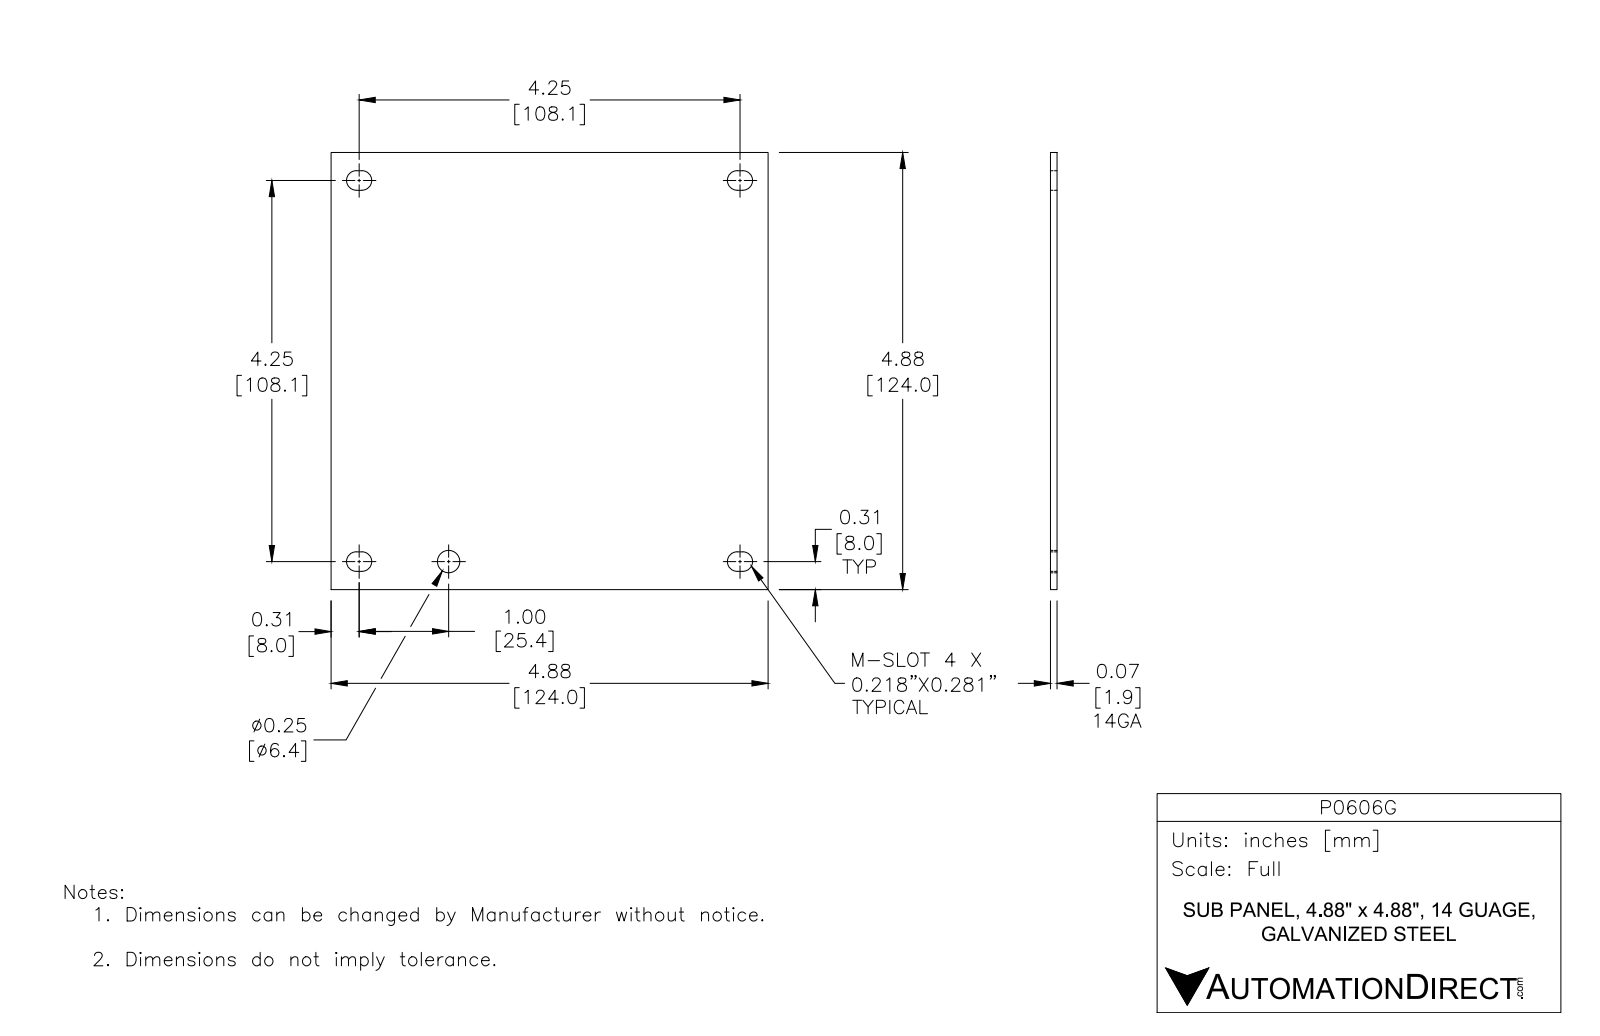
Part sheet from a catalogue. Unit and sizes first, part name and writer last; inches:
Units: inches
Overall size (bounding box): 4.88 × 4.88 × 0.074
Round holes (diameter × count): ⌀0.25 ×1
Partial cylindrical surfaces — rounded edges, fillets, slot ends (radius × count): R0.109 ×8
Main face-to-face distances: 0.074, 4.88, 0.204, 0.422, 4.458, 4.676, 0.218, 4.254, 4.472, 4.036
Volume: 1.744 in³ · Surface area: 48.86 in²
Bodies: 1 solid, 23 faces (14 planar, 9 cylindrical, 0 other)
Part name (STEP PRODUCT): P0606G
STEP written by: Autodesk Inventor 2012 (AUTOMOTIVE_DESIGN)
